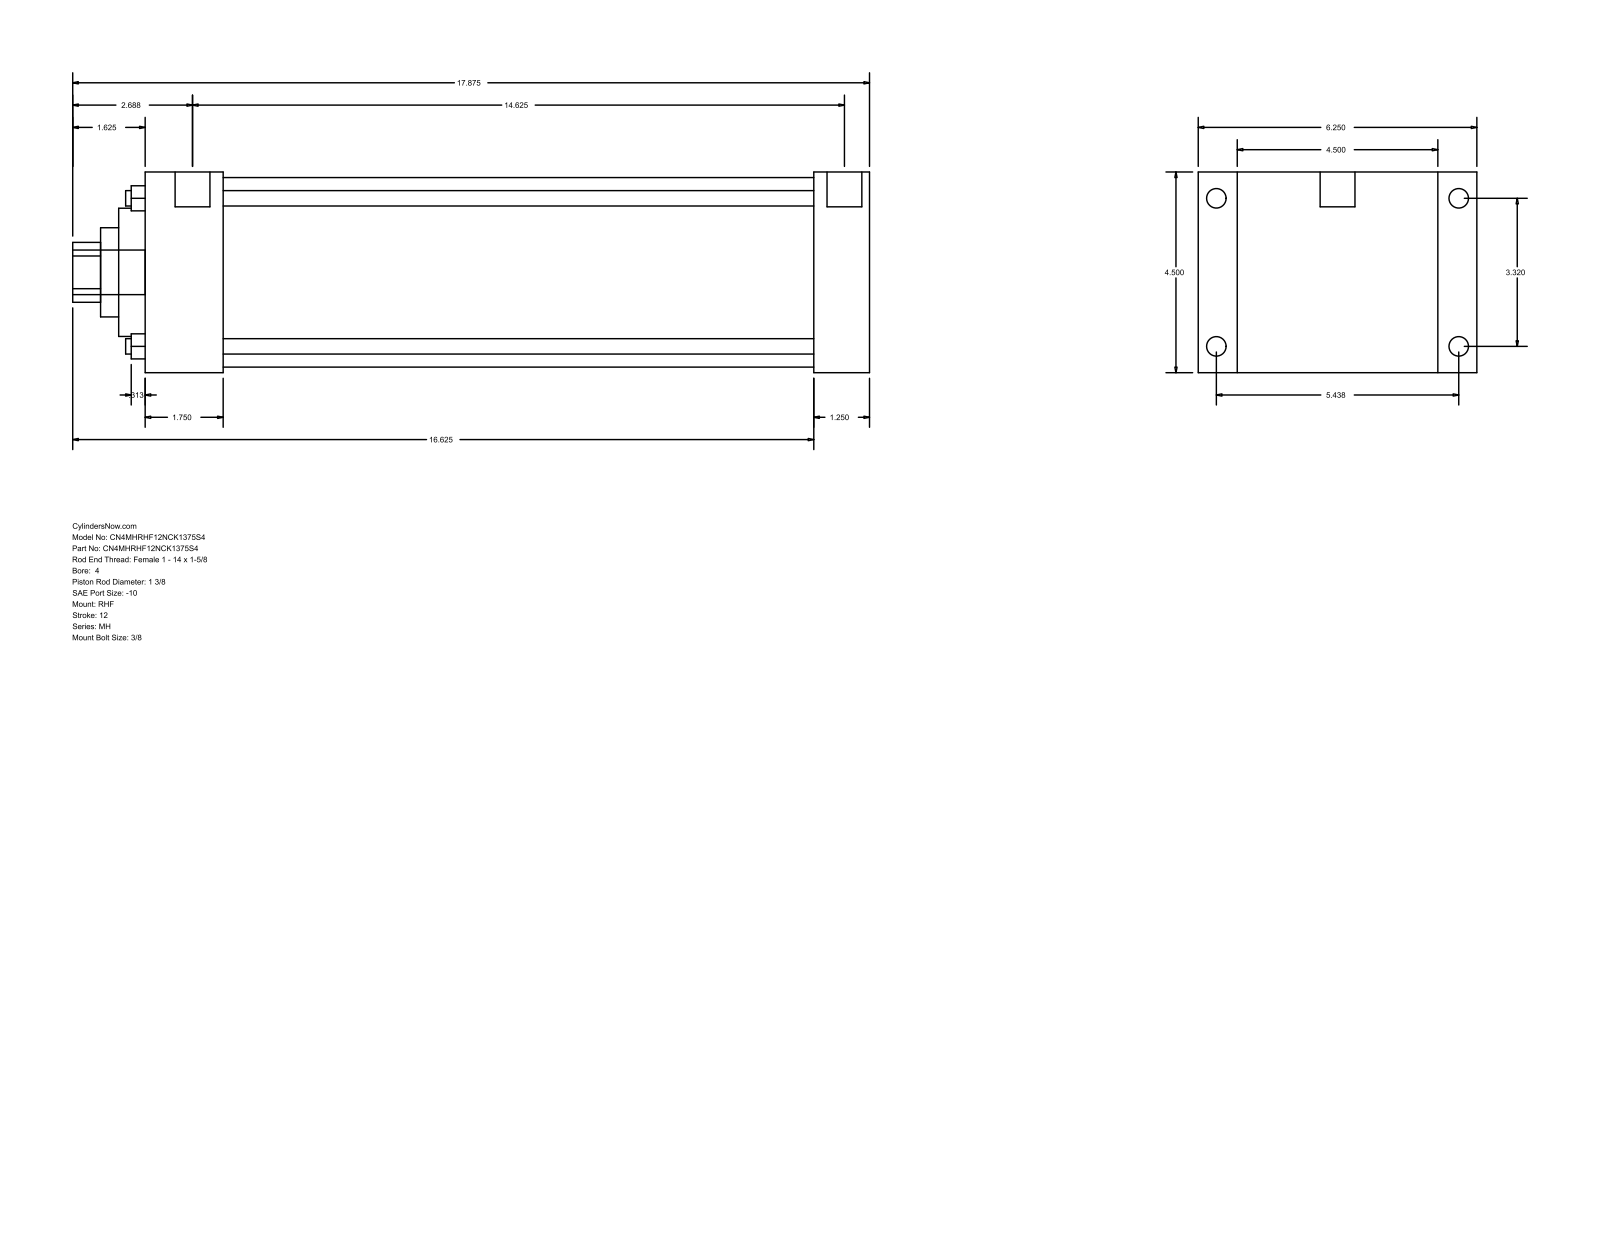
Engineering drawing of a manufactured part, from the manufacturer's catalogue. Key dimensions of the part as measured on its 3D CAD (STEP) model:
Part name (STEP PRODUCT): MH_RHF__0400_1.375
STEP written by: GSSL Pune (CONFIG_CONTROL_DESIGN)
Units: millimetres
Bodies: 0 solids, 90 faces (61 planar, 29 cylindrical, 0 other)
Overall size (bounding box): 454.02 × 158.75 × 114.3
Round holes (diameter × count): ⌀8.76 ×4, ⌀34.92 ×1, ⌀50.8 ×1, ⌀73.03 ×1, ⌀107.95 ×1
Round bosses / shafts (diameter × count): ⌀11.13 ×4, ⌀8.73 ×4, ⌀19.84 ×2, ⌀25.4 ×1
Partial cylindrical surfaces — rounded edges, fillets, slot ends (radius × count): R17.06 ×1
Main face-to-face distances: 114.3, 412.75, 381, 31.75, 22.23, 136.53, 44.45, 336.55, 368.3, 158.76
Hole centre spacings: 59.62, 84.32, 119.25
